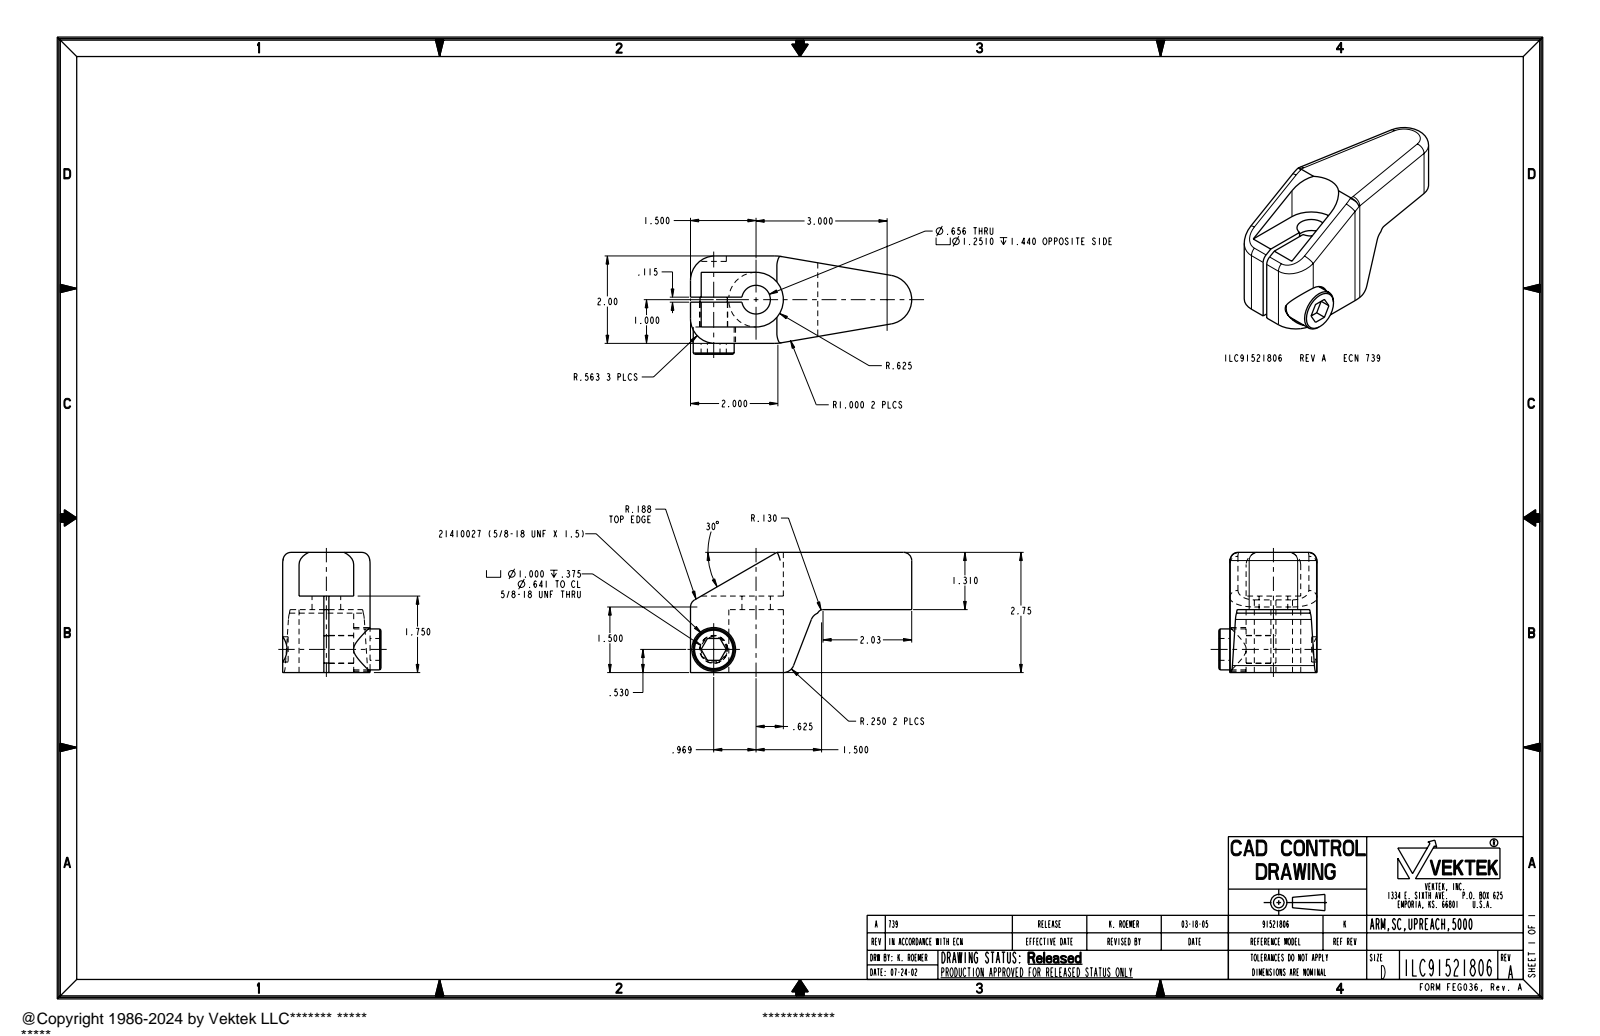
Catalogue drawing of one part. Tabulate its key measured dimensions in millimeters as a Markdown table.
| quantity | value |
| --- | --- |
| part name | ILC91521806 |
| STEP written by | PRO/ENGINEER BY PARAMETRIC TECHNOLOGY CORPORATION, 2004290 (AUTOMOTIVE_DESIGN_CC2) |
| units | millimeters |
| bodies | 1 solid, 67 faces (30 planar, 28 cylindrical, 9 other) |
| overall size | 128.6 × 69.9 × 57.2 |
| volume | 208 900 mm³ |
| surface area | 35 740 mm² |
| round holes (diameter × count) | 14.7 × 1, 16.3 × 1, 16.7 × 1, 25.4 × 1, 31.8 × 1 |
| round bosses / shafts (diameter × count) | 23.8 × 1, 15.9 × 1 |
| partial cylindrical surfaces (radius × count) | 4.8 × 7, 14.3 × 3, 6.4 × 2, 3.3 × 1, 15.9 × 1, 25.4 × 1 |
| main face-to-face distances | 33.3, 69.9, 36.6, 50.8, 24, 26.8, 25.4, 7.9, 44.5, 2.9 |
